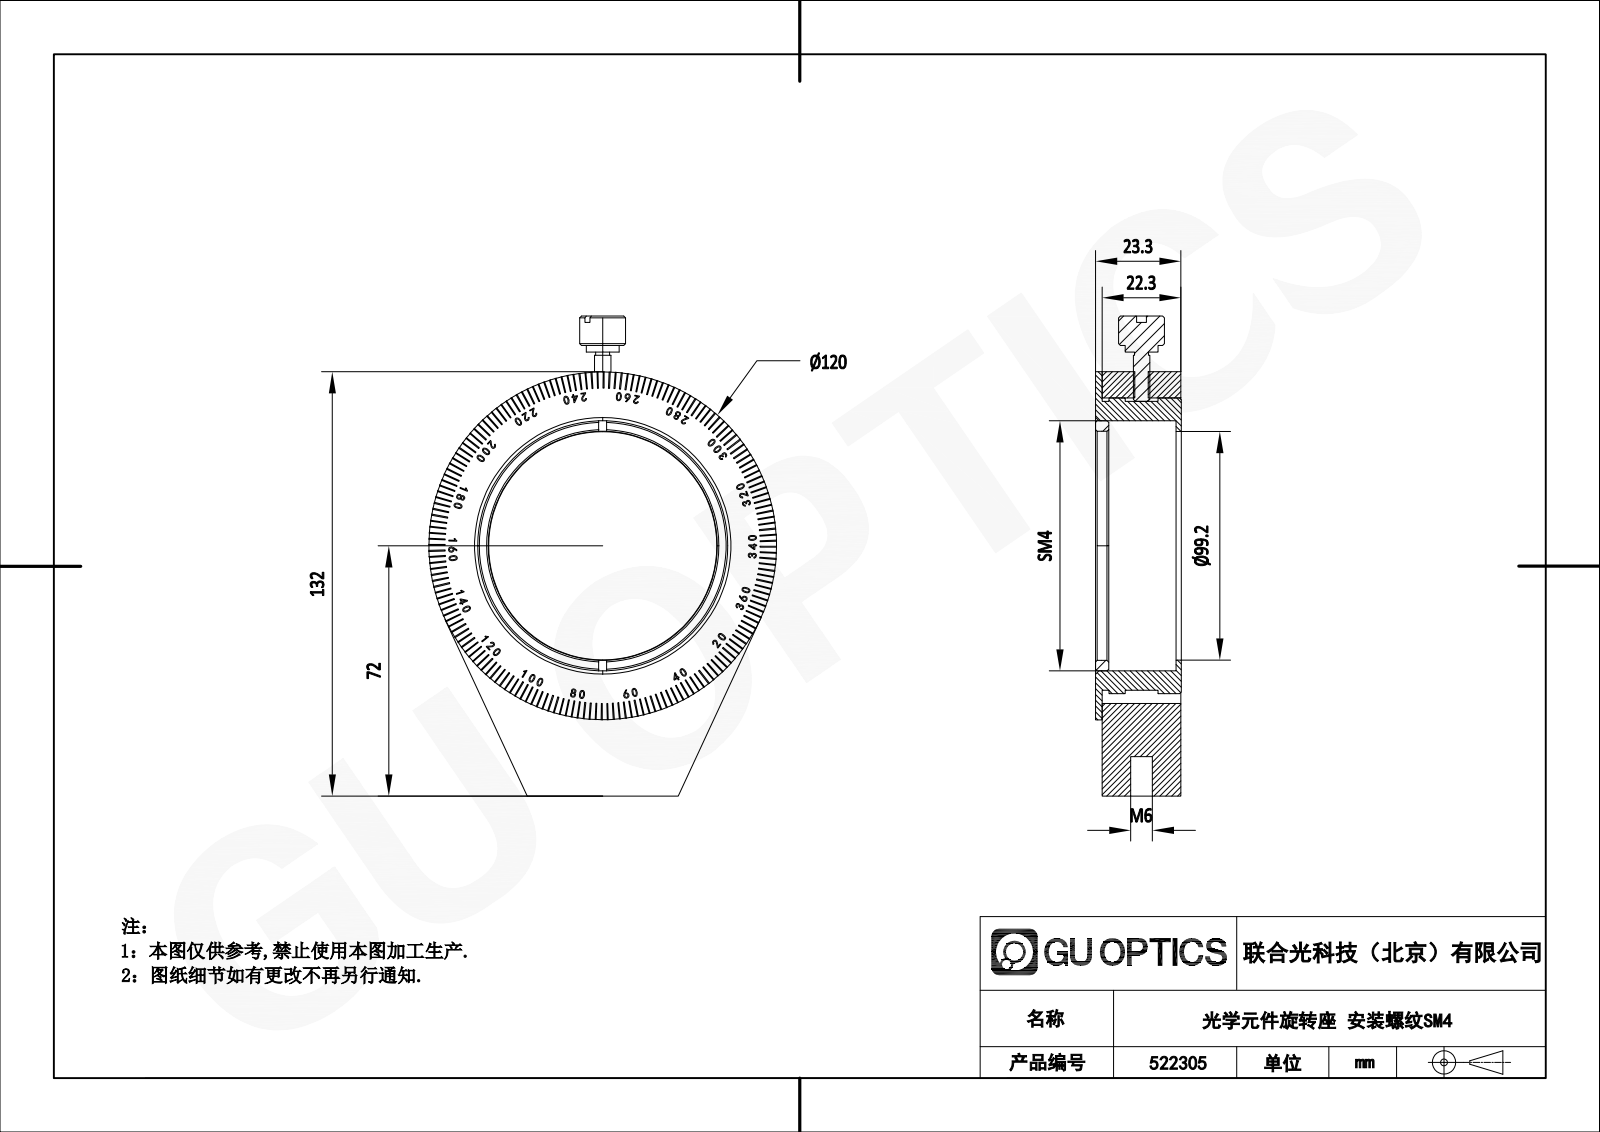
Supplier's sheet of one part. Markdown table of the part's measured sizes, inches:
| quantity | value |
| --- | --- |
| part name | 522305 |
| STEP written by | SolidWorks 2020 (CONFIG_CONTROL_DESIGN) |
| units | inches |
| bodies | 4 solids, 2404 faces (1991 planar, 67 cylindrical, 346 other) |
| overall size | 5.445 × 4.724 × 0.917 |
| volume | 5.204 in³ |
| surface area | 74.15 in² |
| round holes (diameter × count) | 0.081 × 1, 0.197 × 1, 3.811 × 1, 3.906 × 1, 4 × 1, 4.063 × 1 |
| round bosses / shafts (diameter × count) | 4.724 × 1, 4.26 × 1, 4.197 × 1, 4.035 × 1, 0.098 × 1, 0.083 × 1 |
| partial cylindrical surfaces (radius × count) | 0.138 × 1, 2.067 × 1 |
| main face-to-face distances | 0.78, 0.138, 0.917, 0.039, 0.74, 0.459, 0.787, 0.13, 0.748, 0.878 |
